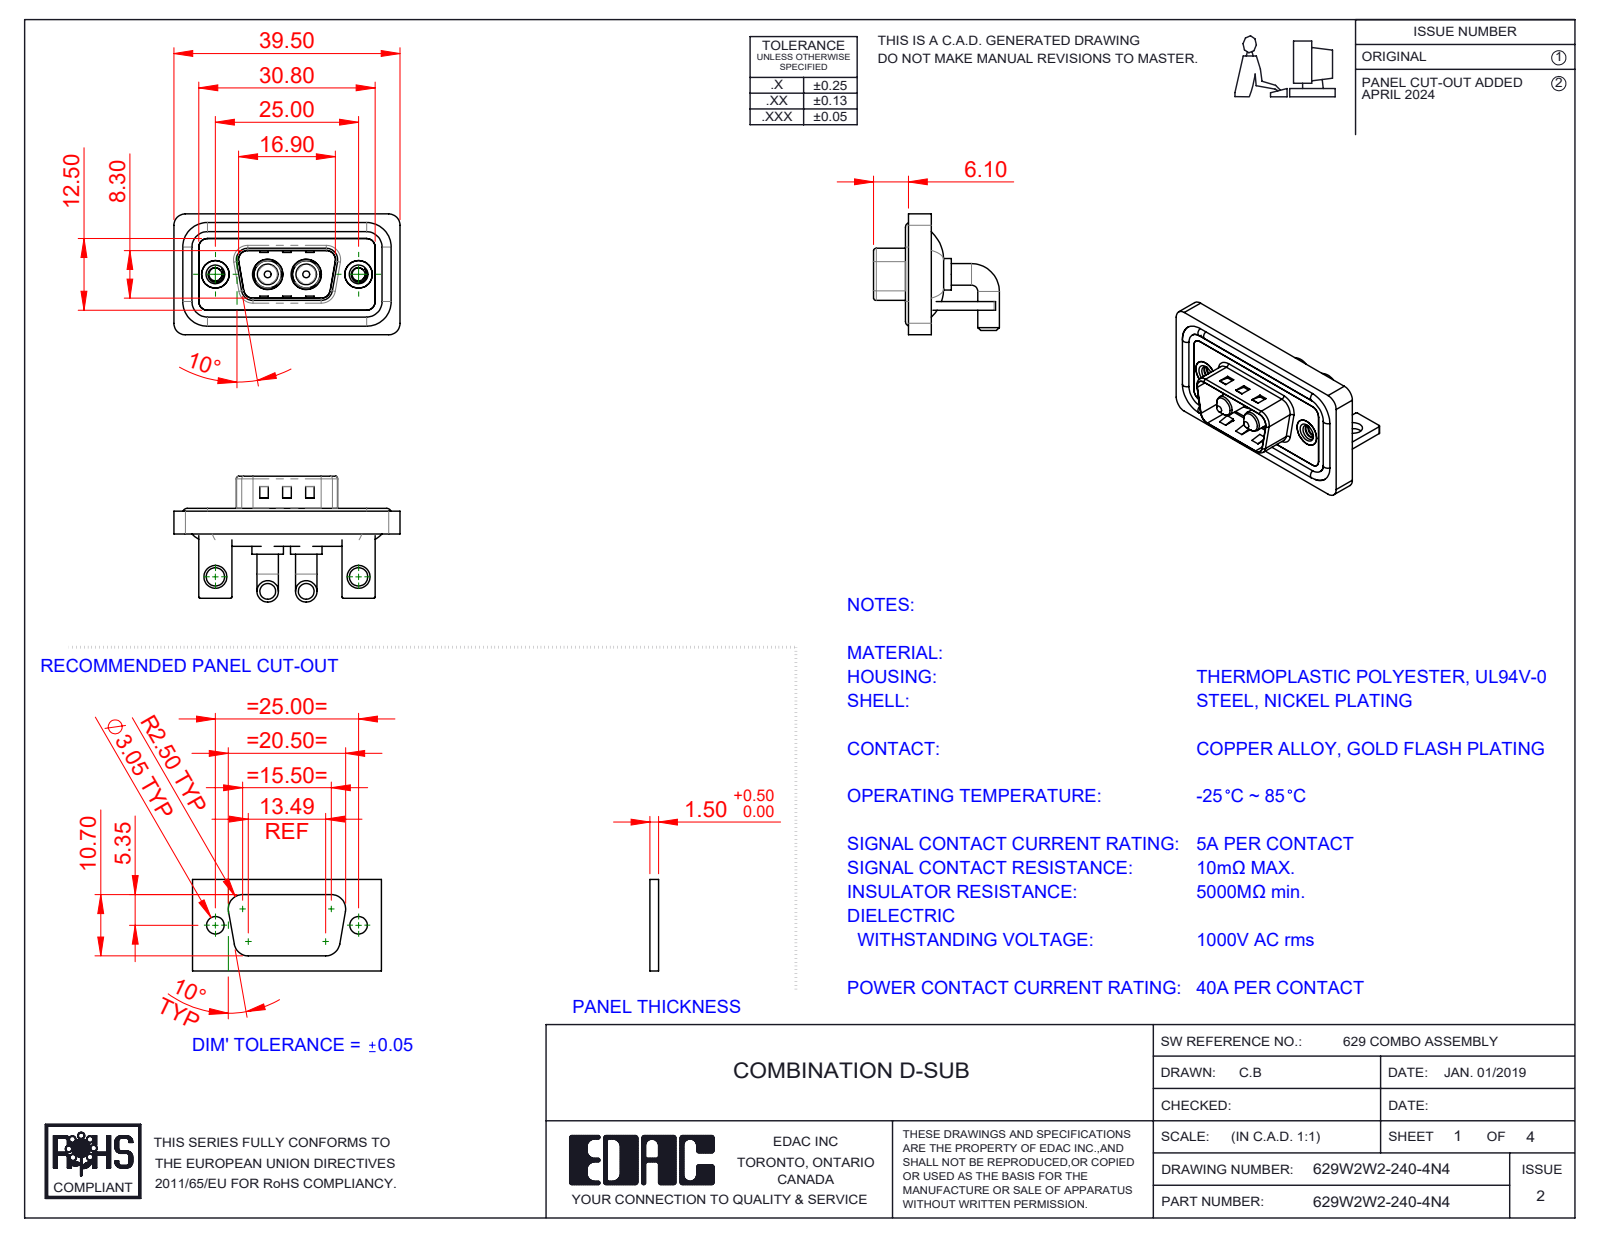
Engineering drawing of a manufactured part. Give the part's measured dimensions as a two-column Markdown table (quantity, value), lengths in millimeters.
| quantity | value |
| --- | --- |
| part name | 629Combo Shell Rear_09 Contacts; Power Pin_40A RA; 629Combo Threaded Rivet_3; 629Combo Shell Front_09 Contacts (+4 more) |
| STEP written by | SolidWorks 2023 (CONFIG_CONTROL_DESIGN) |
| units | millimeters |
| bodies | 13 solids, 537 faces (185 planar, 240 cylindrical, 112 other) |
| overall size | 39.5 × 21.98 × 21.1 |
| volume | 5 008 mm³ |
| surface area | 7 842 mm² |
| round holes (diameter × count) | 2.26 × 2, 3.2 × 2, 4 × 2, 4.8 × 2, 4.85 × 2, 5 × 2, 5.3 × 2 |
| round bosses / shafts (diameter × count) | 3.75 × 4, 1.6 × 4, 5.5 × 2, 5.2 × 2, 4.9 × 2, 4.75 × 2, 3.6 × 2 |
| partial cylindrical surfaces (radius × count) | 2 × 19, 1.5 × 18, 0.25 × 16, 0.5 × 9, 1.6 × 8, 0.6 × 4, 0.65 × 4, 0.9 × 4 |
| main face-to-face distances | 0.4, 1.5, 2.9, 0.8, 1.1, 1.2, 2.1, 1.6, 3.7, 2.5 |
| hole center spacings | 9.14, 15.86, 25, 6.72 |
